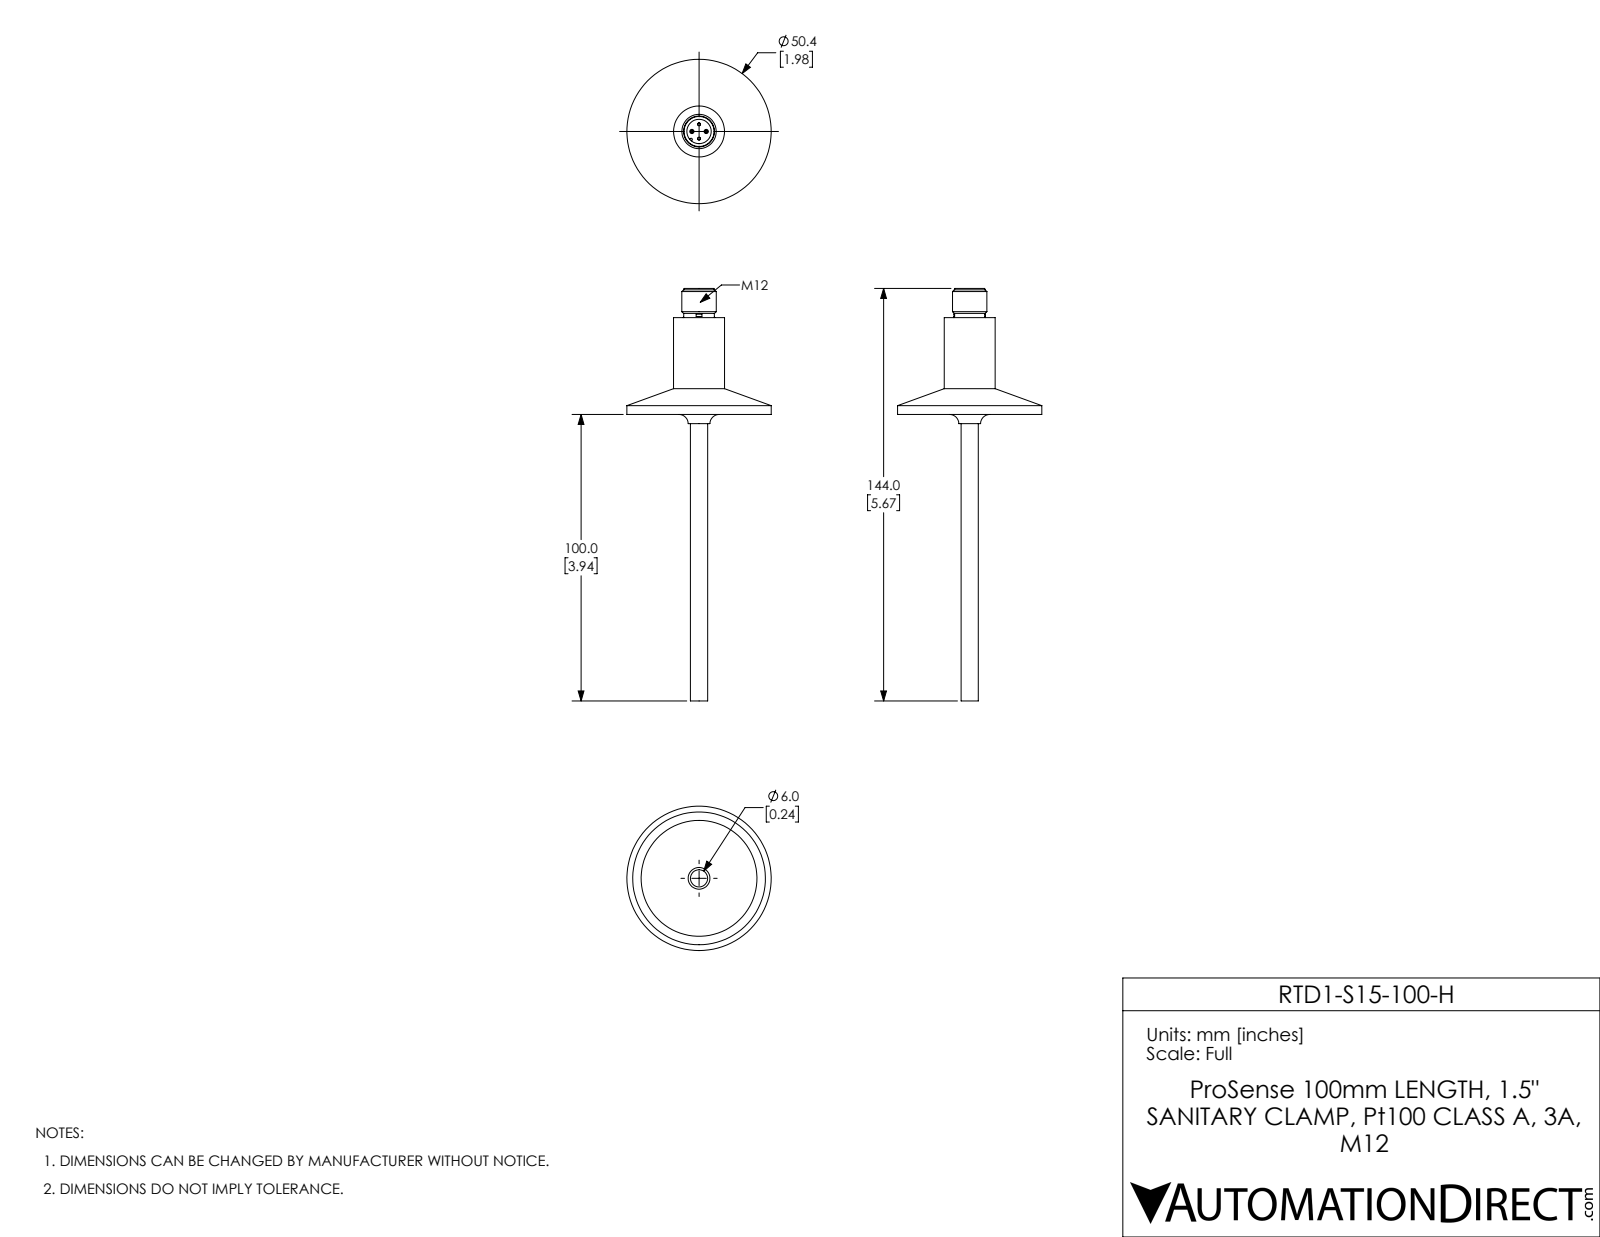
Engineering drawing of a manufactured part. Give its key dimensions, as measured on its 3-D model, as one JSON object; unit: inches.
{"part_name": "RTD1-S15-100-H", "step_written_by": "SolidWorks 2017 (AUTOMOTIVE_DESIGN)", "units": "inches", "bodies": {"solids": 1, "faces": 79, "planar": 26, "cylindrical": 23, "other": 30}, "overall_size": [5.669, 1.984, 1.984], "volume_in3": 1.294, "surface_area_in2": 13.6, "round_holes": [[0.335, 1]], "round_bosses_or_shafts": [[0.04, 4], [1.984, 1], [0.701, 1], [0.472, 1], [0.421, 1], [0.413, 1], [0.236, 1]], "partial_cylinders_radius": [[0.016, 1]], "face_to_face_distances": [1.331, 1.378, 0.047, 1.732, 0.402, 0.354, 3.937, 5.268, 5.315, 5.669]}
